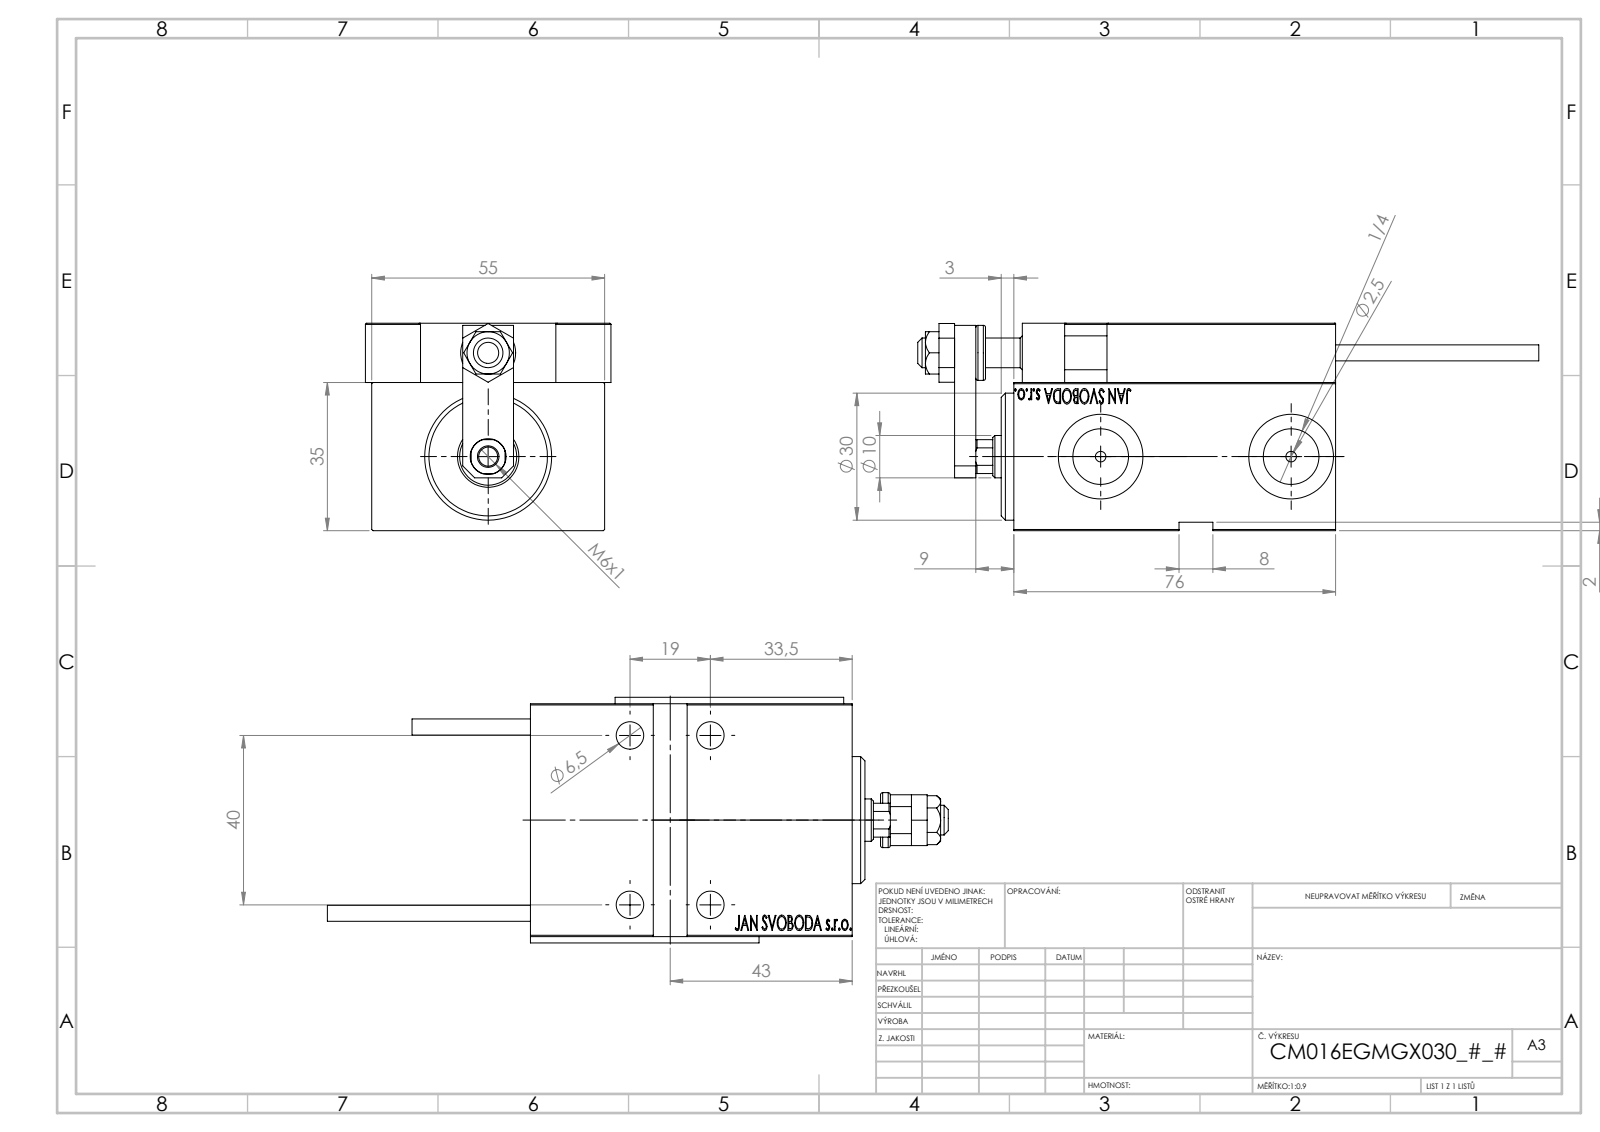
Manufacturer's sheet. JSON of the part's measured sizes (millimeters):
{"part_name": "NUT_D12; V450CM_E_Body; V450CM_E_VCP; Block (+7 more)", "step_written_by": "SolidWorks 2019 (CONFIG_CONTROL_DESIGN)", "units": "millimeters", "bodies": {"solids": 24, "faces": 1299, "planar": 572, "cylindrical": 186, "other": 541}, "overall_size": [146.7, 58, 49], "volume_mm3": 175117, "surface_area_mm2": 54496, "round_holes": [[8, 5], [3.2, 4], [4, 4], [6.5, 4], [10.5, 4], [2.5, 2], [5, 2], [13.16, 2], [20, 2], [4.5, 1], [7, 1], [8.5, 1]], "round_bosses_or_shafts": [[5, 2], [3.8, 2], [30, 1], [13, 1], [11, 1]], "partial_cylinders_radius": [[0.3, 30], [3, 2], [4.5, 1]], "face_to_face_distances": [35, 14, 49, 10, 5, 55, 1.5, 3, 76, 45], "hole_center_spacings": [11.37, 12.42, 19, 20, 21.03, 28.07, 28.32, 29.59]}
